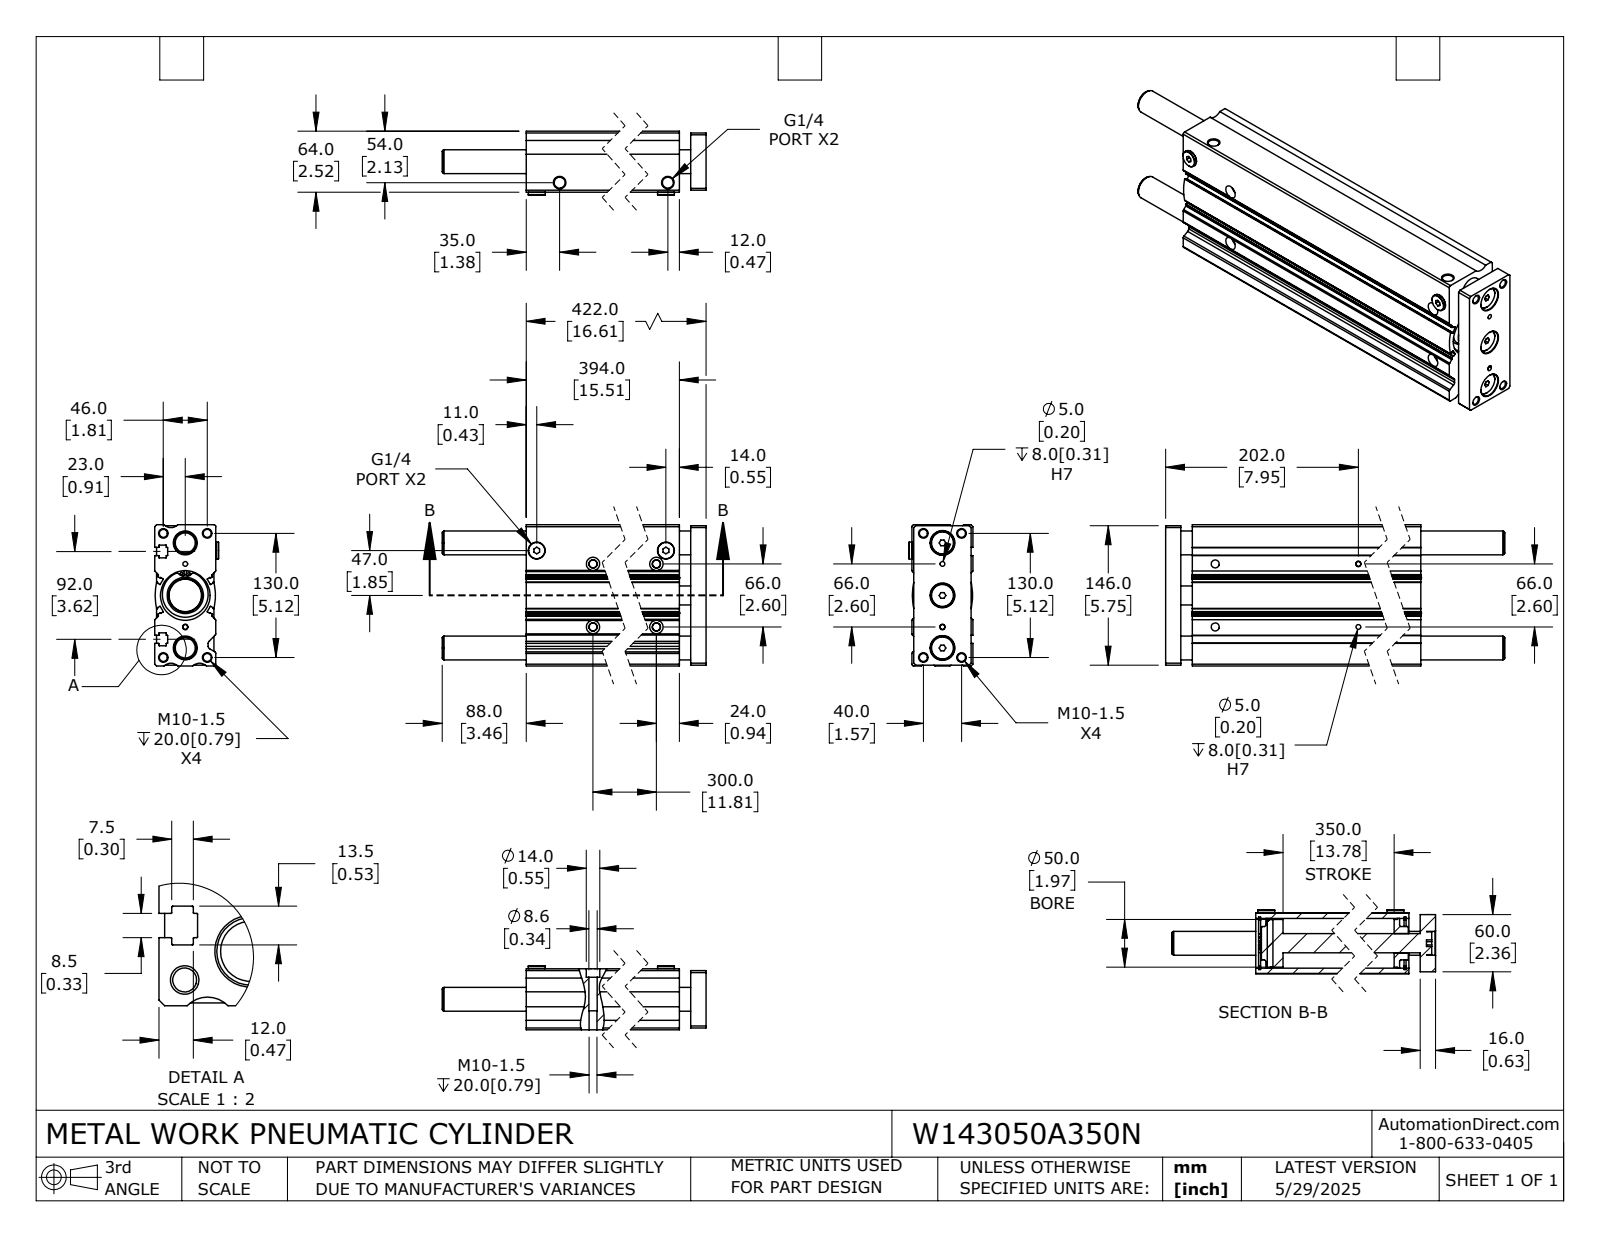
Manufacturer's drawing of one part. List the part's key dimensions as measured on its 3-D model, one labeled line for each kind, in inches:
Part name (STEP PRODUCT): W143050A350N_ROD; W143050A350N_BODY; W143050A350N
STEP written by: SolidWorks 2024 (CONFIG_CONTROL_DESIGN)
Units: inches
Bodies: 6 solids, 466 faces (186 planar, 224 cylindrical, 56 other)
Overall size (bounding box): 20.079 × 5.827 × 2.638
Volume: 181.2 in³ · Surface area: 807.5 in²
Round holes (diameter × count): ⌀0.33 ×12, ⌀0.098 ×4, ⌀0.197 ×4, ⌀0.339 ×4, ⌀0.551 ×4, ⌀0.984 ×3, ⌀0.451 ×2, ⌀1.89 ×2, ⌀0.787 ×1
Round bosses / shafts (diameter × count): ⌀0.945 ×3, ⌀0.697 ×2, ⌀2.165 ×1, ⌀2.047 ×1, ⌀1.969 ×1, ⌀1.378 ×1
Partial cylindrical surfaces — rounded edges, fillets, slot ends (radius × count): R0.012 ×44, R0.02 ×12, R0.118 ×10, R0.079 ×6, R2.677 ×6, R0.039 ×4, R0.098 ×4, R0.394 ×3
Main face-to-face distances: 2.52, 0.472, 5.827, 0.531, 0.098, 3.622, 0.433, 15.512, 0.63, 1.988
Hole centre spacings: 0.118, 0.424, 0.869, 0.88, 0.916, 0.963, 0.987, 1.271
